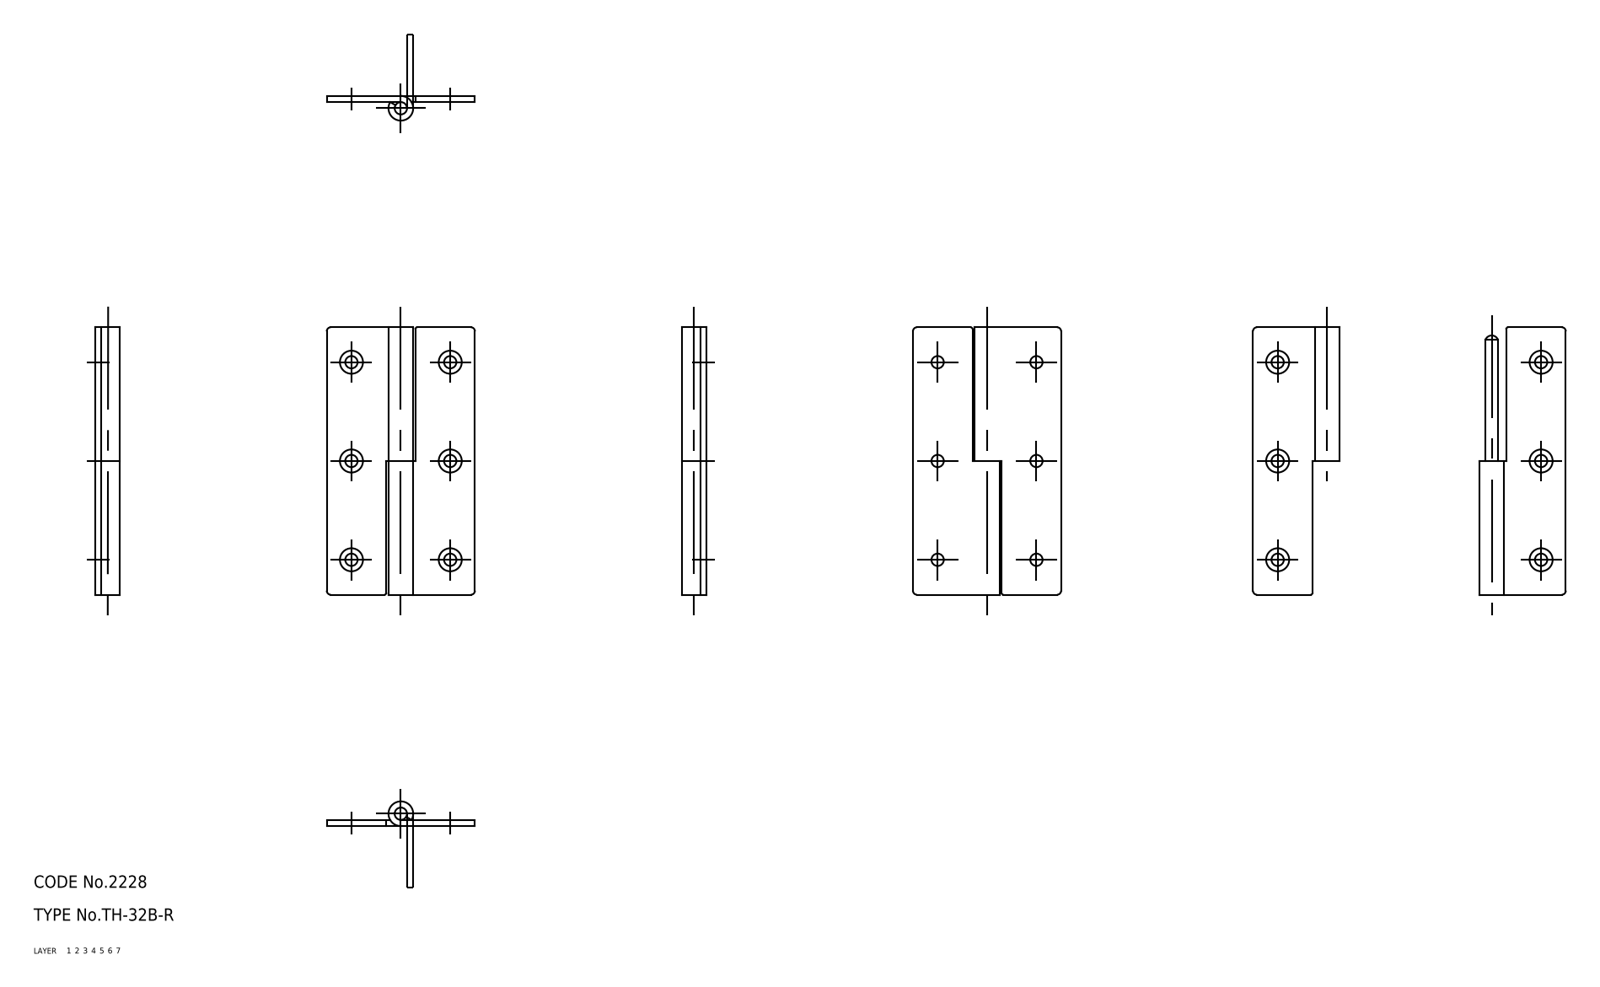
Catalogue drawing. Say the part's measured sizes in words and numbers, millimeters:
The part is named "shaft; hinge piece_B; hinge piece_A; TH_32B_R_7801_36". Its 3-D file was written by "CADfix (AUTOMOTIVE_DESIGN)". It is 3 solids with 54 faces: 0 planar, 0 cylindrical and 54 other. Overall it measures 65 by 36 by 6 millimeters. Its volume is 4 630 cubic millimeters and its surface area 6 887 square millimeters.
